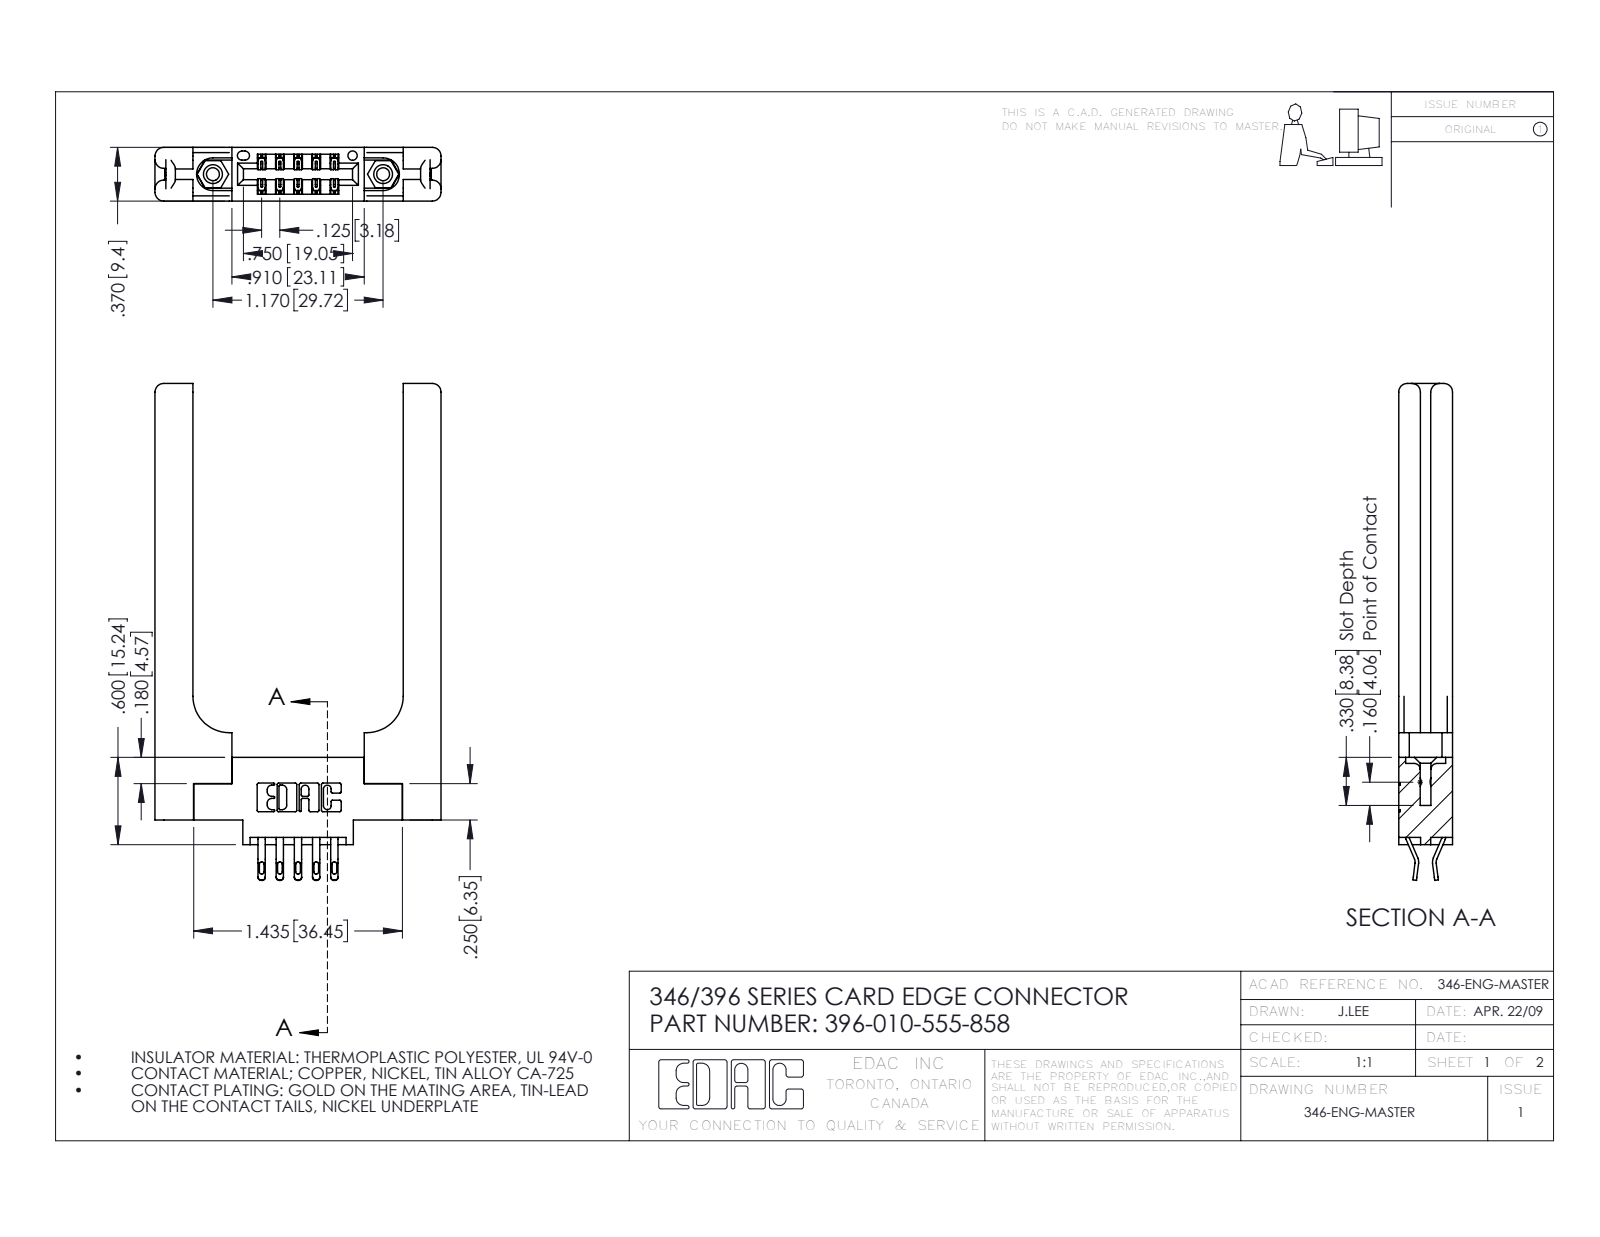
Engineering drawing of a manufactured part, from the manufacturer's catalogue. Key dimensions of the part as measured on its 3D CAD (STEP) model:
Part name (STEP PRODUCT): 346-220-058_345-220-058; 345-292-001_555 Tail; 396-010-555-858; 345-250-001_345-250-001-102 (+1 more)
STEP written by: SolidWorks 2016 (CONFIG_CONTROL_DESIGN)
Units: inches
Bodies: 15 solids, 962 faces (558 planar, 344 cylindrical, 60 other)
Overall size (bounding box): 3.415 × 1.966 × 0.37
Volume: 0.729 in³ · Surface area: 16.74 in²
Round holes (diameter × count): ⌀0.089 ×2, ⌀0.125 ×2, ⌀0.156 ×2, ⌀0.064 ×1
Round bosses / shafts (diameter × count): ⌀0.155 ×2
Partial cylindrical surfaces — rounded edges, fillets, slot ends (radius × count): R0.01 ×22, R0.016 ×20, R0.02 ×20, R0.06 ×16, R0.006 ×15, R0.007 ×6, R0.031 ×6, R0.026 ×3
Main face-to-face distances: 0.37, 0.15, 0.22, 0.25, 0.072, 1.446, 0.148, 0.075, 0.071, 0.26
Hole centre spacings: 0.246, 0.969, 1.17
